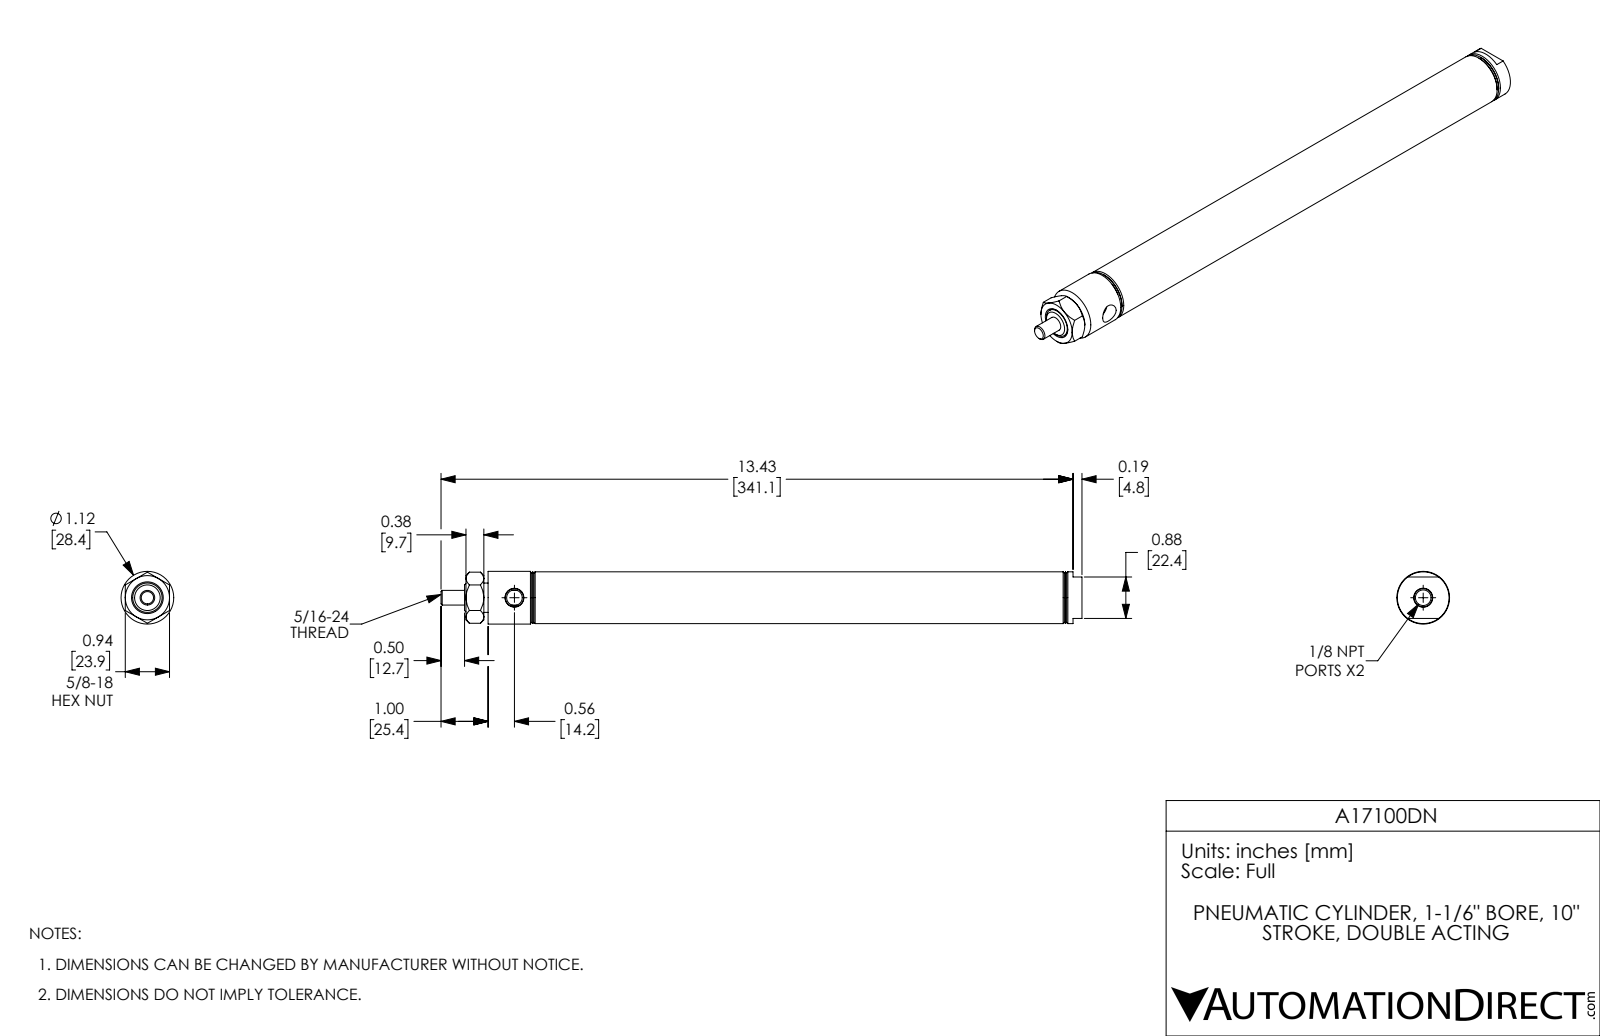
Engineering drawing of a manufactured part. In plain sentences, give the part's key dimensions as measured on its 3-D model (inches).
The part is named "A17100DN; A17100DN_Mounting Nut_D-9; A17100DN-Rod; A17100DN-MainBody". Its 3-D file was written by "SolidWorks 2017 (AUTOMOTIVE_DESIGN)". It is 3 solids with 94 faces: 24 planar, 26 cylindrical and 44 other. Overall it measures 13.62 by 1.12 by 1.12 inches. Its volume is 4.121 cubic inches and its surface area 104.3 square inches. Round holes: 2 of diameter 0.332, 1 of diameter 0.312, 1 of diameter 0.625, 1 of diameter 1.063. Round bosses or shafts: 1 of diameter 1.12, 1 of diameter 1.1, 1 of diameter 0.623. The main face-to-face distances are 0.5, 11.56, 10.5, 10, 1.06, 1.56, 11.56, 12.62, 11.06, 1.06.
